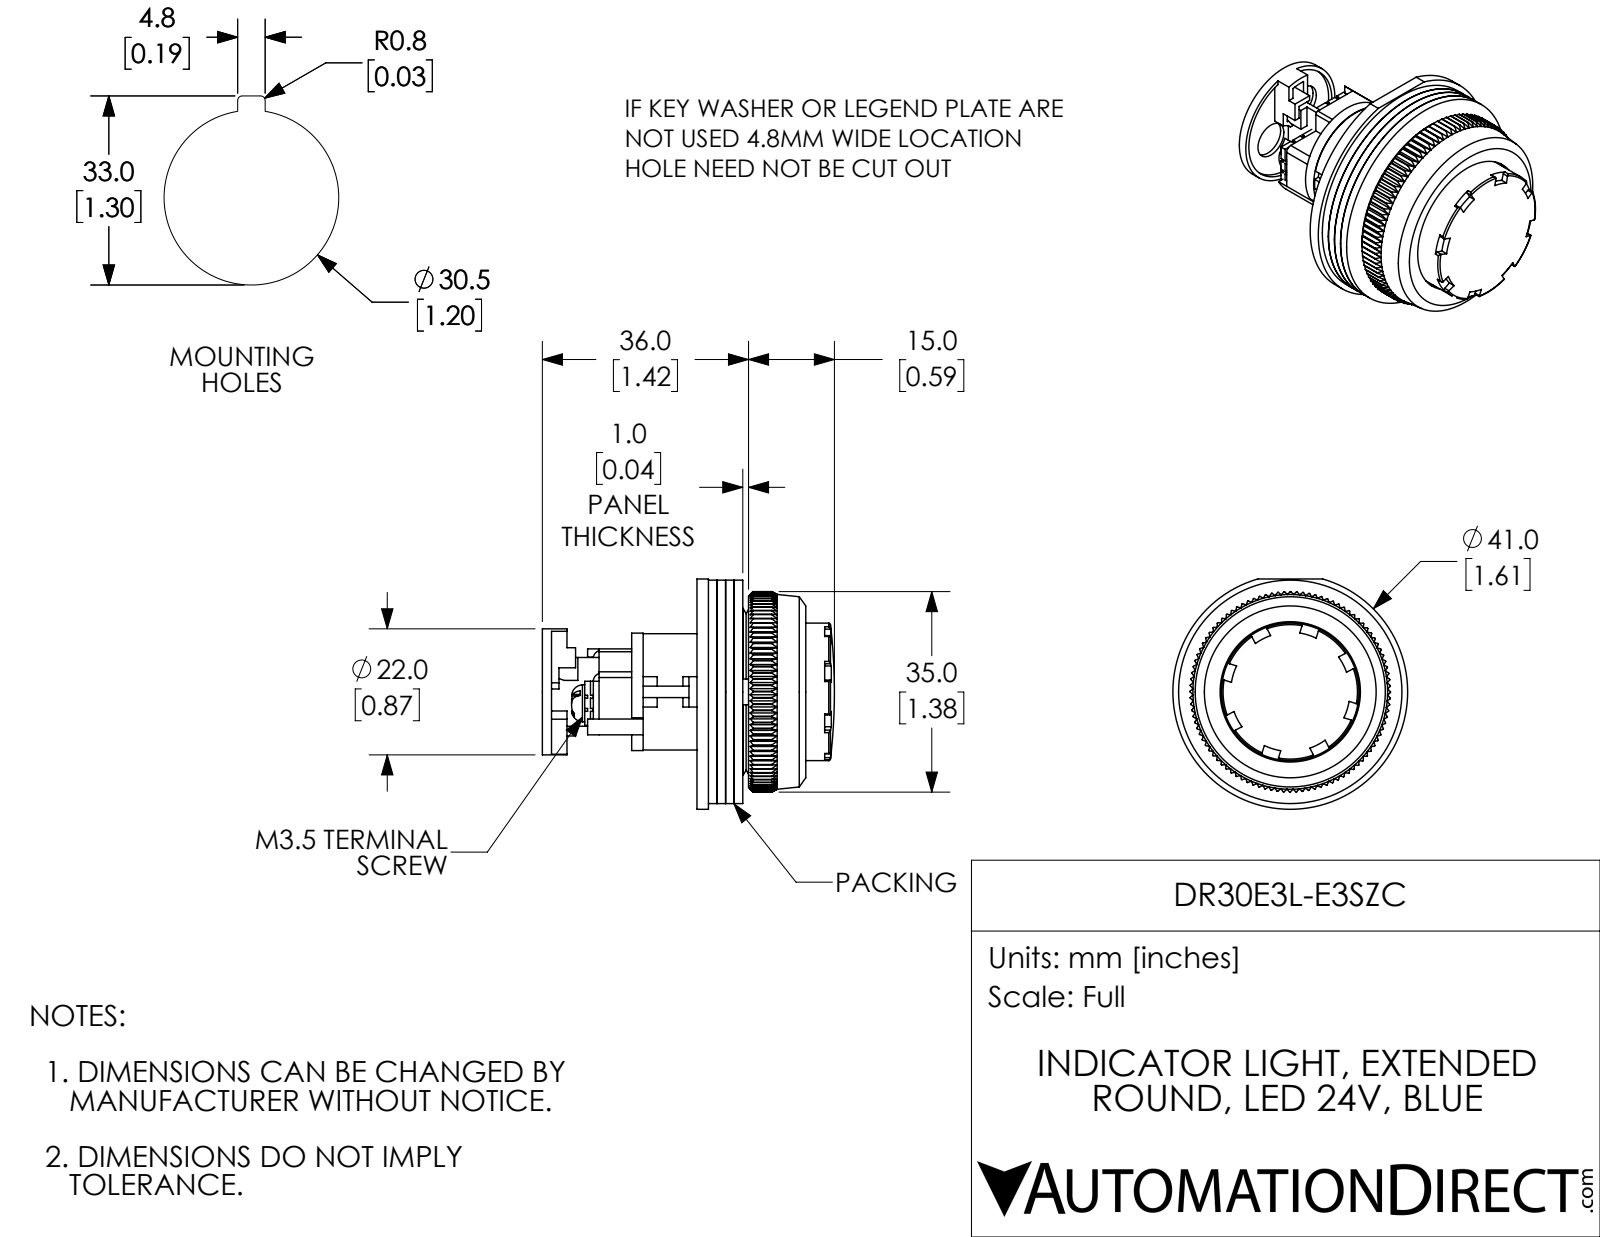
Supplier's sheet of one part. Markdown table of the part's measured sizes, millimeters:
| quantity | value |
| --- | --- |
| part name | DR30E3L-E3SZC |
| STEP written by | SolidWorks 2017 (AUTOMOTIVE_DESIGN) |
| units | millimeters |
| bodies | 16 solids, 1287 faces (717 planar, 328 cylindrical, 242 other) |
| overall size | 51 × 41 × 40.2 |
| volume | 17 570 mm³ |
| surface area | 24 230 mm² |
| round holes (diameter × count) | 3 × 2, 3.5 × 2, 6.4 × 2, 14.3 × 1, 16 × 1, 18.3 × 1, 20 × 1, 20.5 × 1, 22 × 1, 24.5 × 1, 28.5 × 1, 29.8 × 1 |
| round bosses / shafts (diameter × count) | 1.6 × 2, 41 × 1, 39 × 1, 29.5 × 1, 24 × 1, 21.8 × 1, 20.8 × 1, 20.3 × 1 |
| partial cylindrical surfaces (radius × count) | 0.3 × 16, 1.5 × 8, 0.3 × 5, 0.6 × 5, 0.4 × 4, 1.4 × 4, 0.5 × 2, 1 × 2 |
| main face-to-face distances | 1.5, 3, 4.5, 1, 5, 2, 8, 6.5, 2.5, 6 |
| hole center spacings | 4.5, 4.7, 9.2, 8.9, 9.4 |
